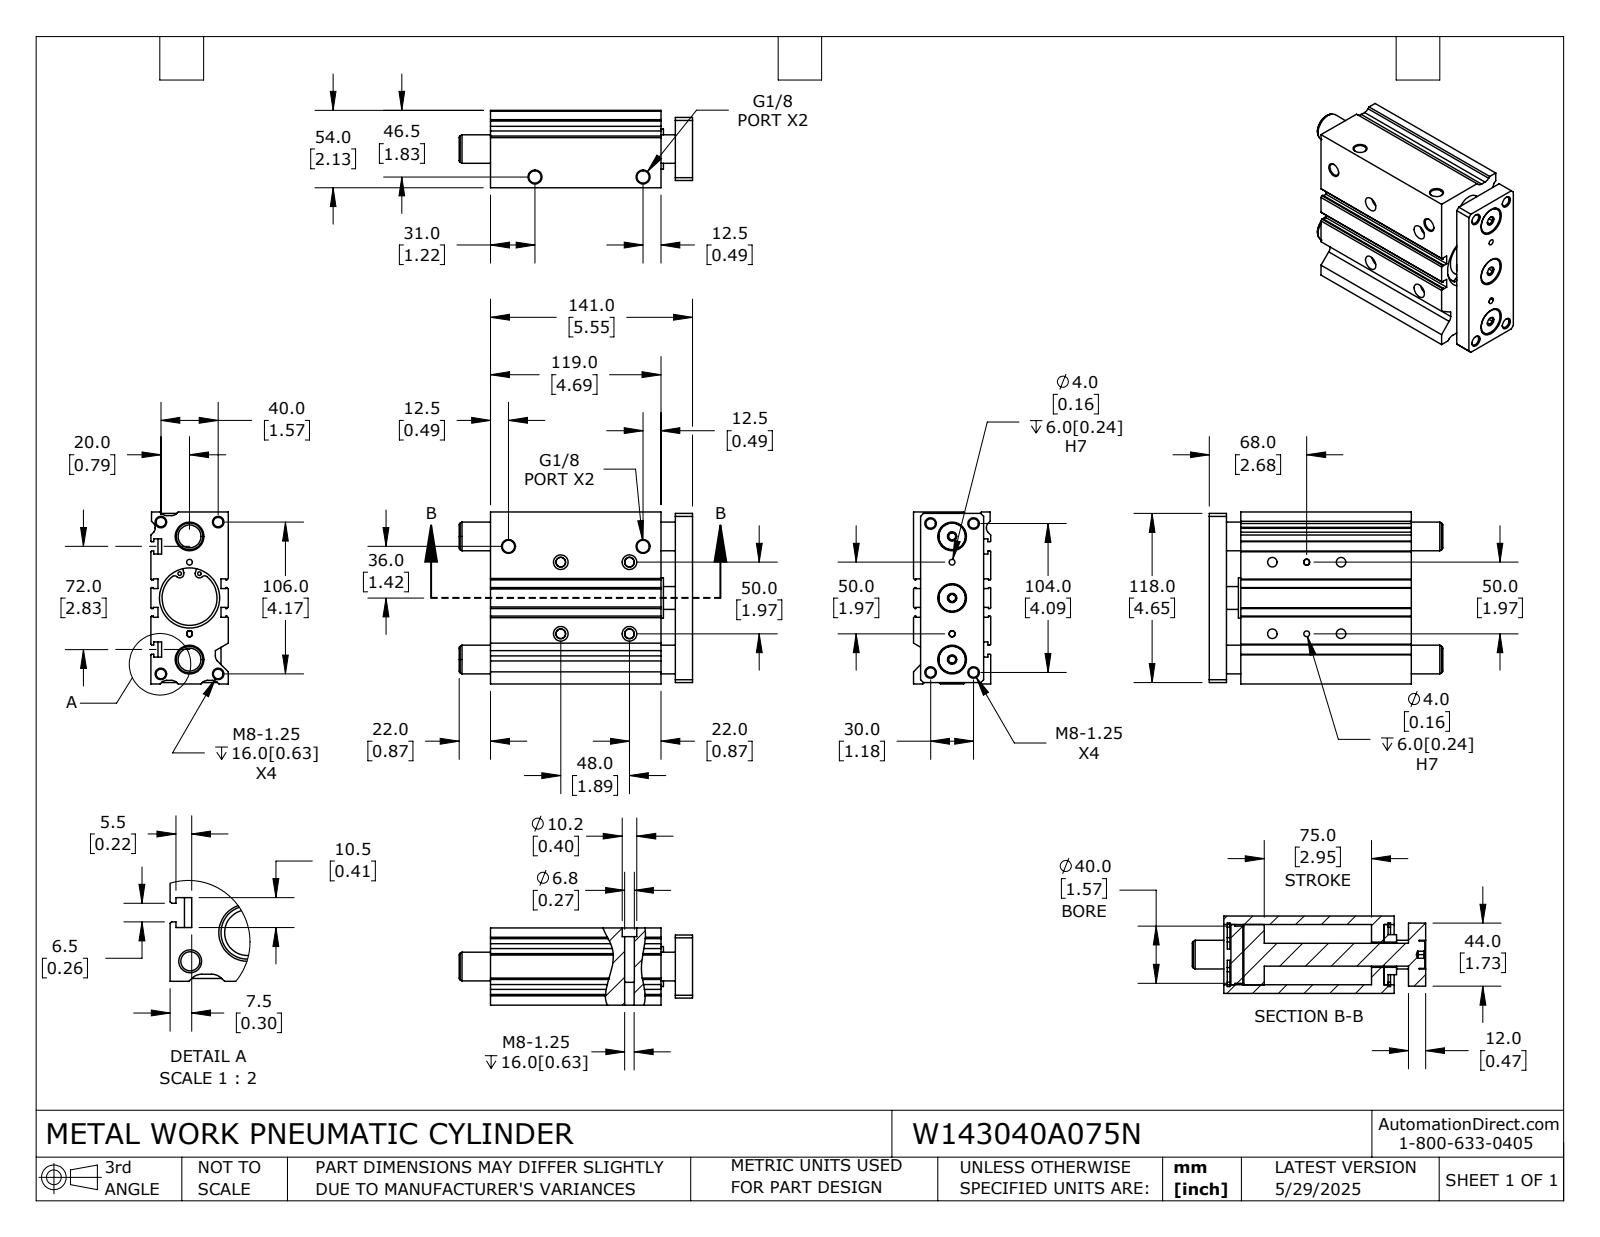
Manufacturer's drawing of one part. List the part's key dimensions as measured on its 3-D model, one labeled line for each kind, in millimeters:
Part name (STEP PRODUCT): W143040A075N_BODY; W143040A075N_ROD; W143040A075N
STEP written by: SolidWorks 2024 (CONFIG_CONTROL_DESIGN)
Units: millimetres
Bodies: 6 solids, 393 faces (192 planar, 151 cylindrical, 50 other)
Overall size (bounding box): 163 × 120 × 54
Volume: 684 300 mm³ · Surface area: 156 700 mm²
Round holes (diameter × count): ⌀6.7 ×12, ⌀2.5 ×4, ⌀4 ×4, ⌀6.8 ×4, ⌀8.6 ×4, ⌀10.2 ×4, ⌀5 ×3, ⌀20 ×3, ⌀17.7 ×1, ⌀38.4 ×1
Round bosses / shafts (diameter × count): ⌀19 ×3, ⌀44.5 ×2, ⌀42 ×1, ⌀40 ×1, ⌀28 ×1, ⌀16 ×1
Partial cylindrical surfaces — rounded edges, fillets, slot ends (radius × count): R5 ×7, R2 ×4, R2.3 ×4, R2.9 ×4, R4 ×2
Main face-to-face distances: 54, 5, 49, 2.5, 119, 22, 141, 12, 10, 129
Hole centre spacings: 5.1, 10.5, 17.5, 18.3, 22.4, 24, 26.9, 30.9
